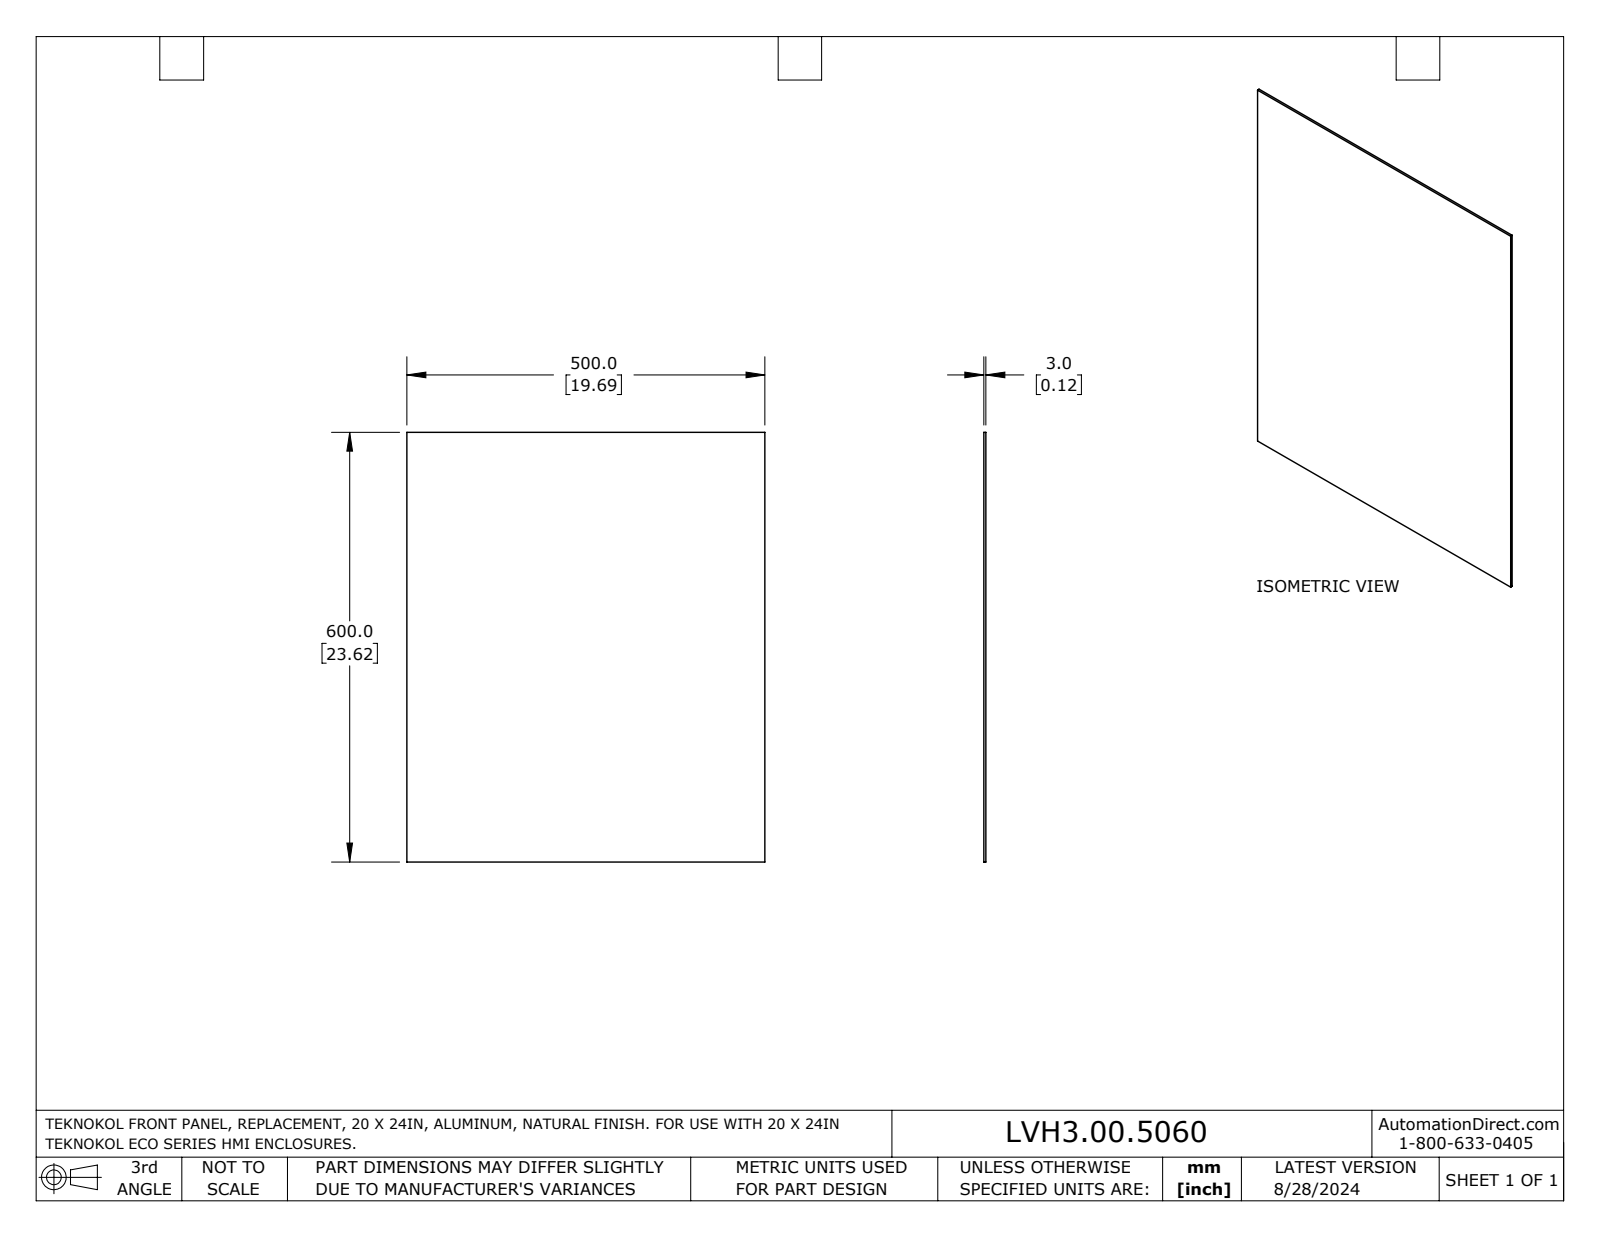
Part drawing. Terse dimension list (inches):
name: LVH3.00.5060(500x600)
written by: SolidWorks 2022 (CONFIG_CONTROL_DESIGN)
unit: in
bodies: 1 solid, 6 faces (6 planar, 0 cylindrical, 0 other)
size: 23.622 × 19.685 × 0.118
volume: 54.92 in³; area: 940.2 in²
face distances: 0.118, 19.685, 23.622
